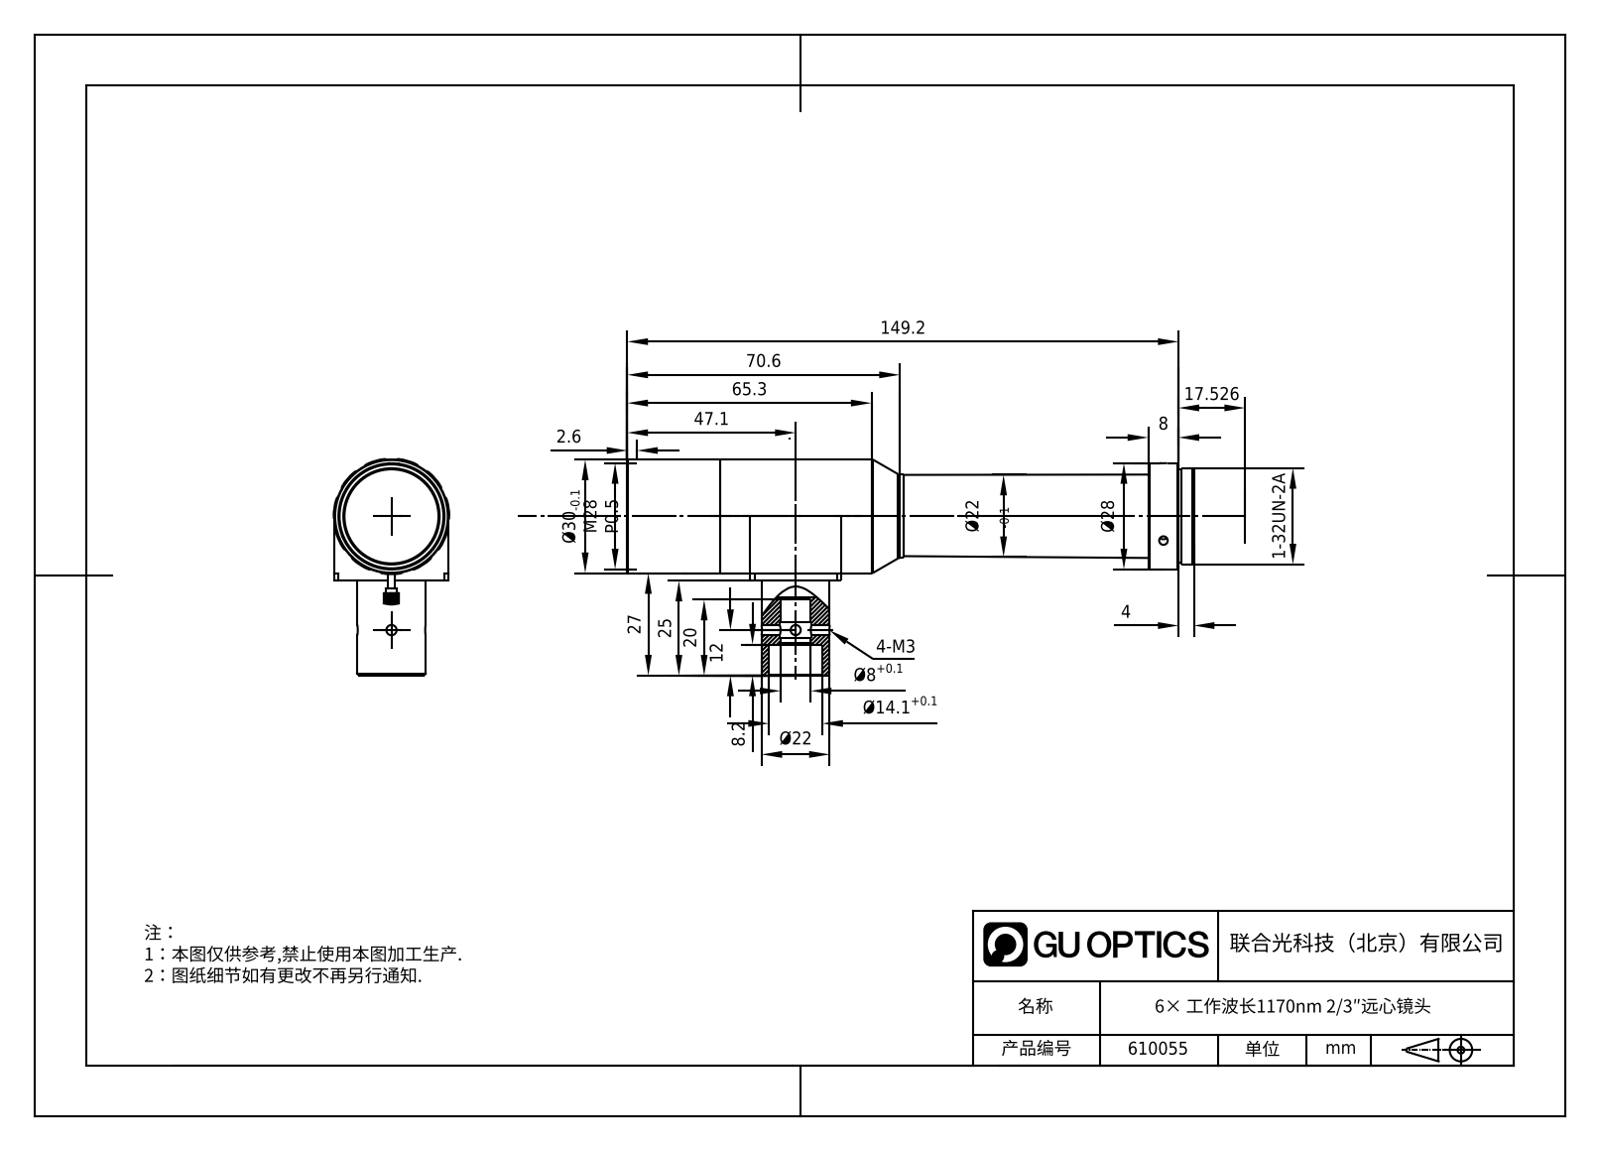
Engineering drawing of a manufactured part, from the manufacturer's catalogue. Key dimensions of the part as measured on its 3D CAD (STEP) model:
Part name (STEP PRODUCT): 610055
STEP written by: SolidWorks 2020 (CONFIG_CONTROL_DESIGN)
Units: millimetres
Bodies: 2 solids, 37 faces (15 planar, 13 cylindrical, 9 other)
Overall size (bounding box): 154.19 × 57 × 30
Volume: 94 426 mm³ · Surface area: 19 139 mm²
Round holes (diameter × count): ⌀2.6 ×2, ⌀8 ×1, ⌀14.1 ×1, ⌀27.5 ×1
Round bosses / shafts (diameter × count): ⌀22 ×2, ⌀30 ×1, ⌀28 ×1, ⌀25.4 ×1, ⌀24.4 ×1
Main face-to-face distances: 150.6, 30, 138.6, 12, 25, 29.8, 108.8, 120.8, 57.8, 28
Hole centre spacings: 30
